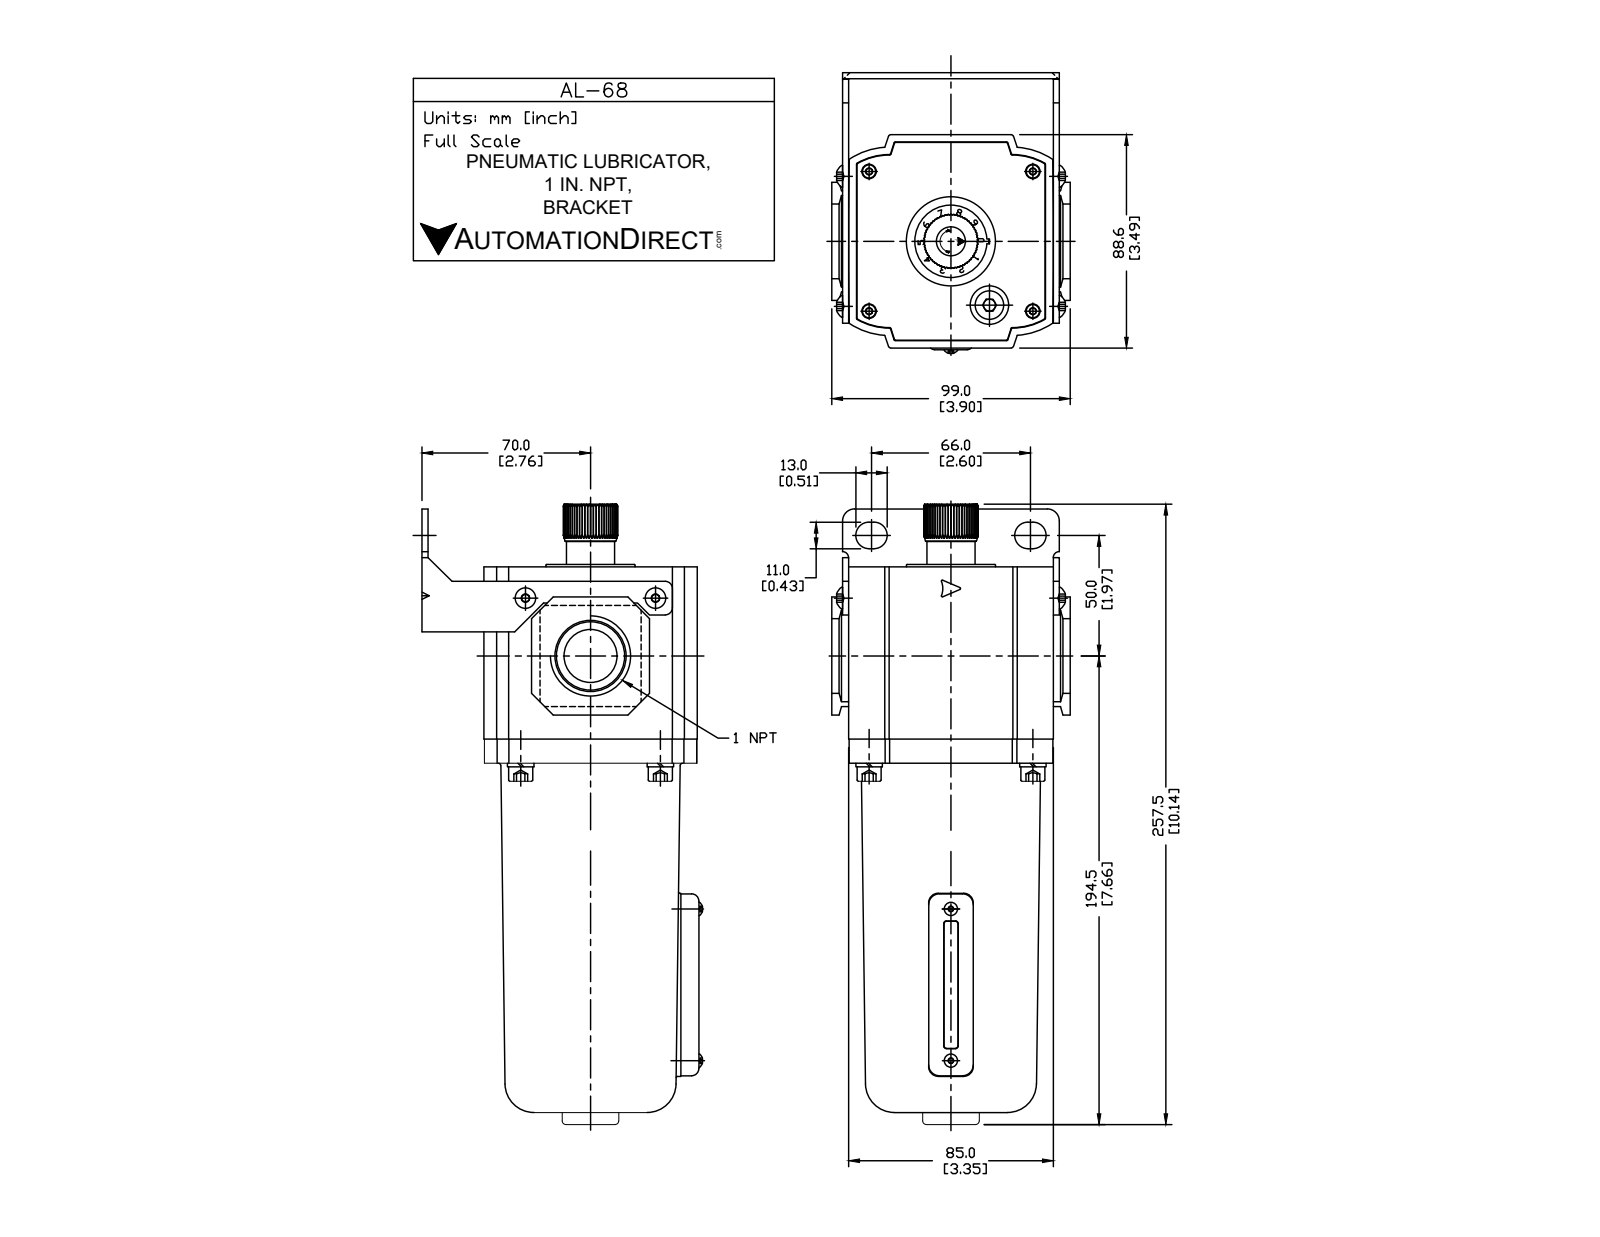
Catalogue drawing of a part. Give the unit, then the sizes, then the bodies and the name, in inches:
Units: inches
Overall size (bounding box): 10.138 × 4.586 × 3.898
Round holes (diameter × count): ⌀0.217 ×2, ⌀1.141 ×1
Round bosses / shafts (diameter × count): ⌀0.394 ×4, ⌀2.933 ×1, ⌀2.362 ×1, ⌀0.925 ×1, ⌀0.787 ×1
Partial cylindrical surfaces — rounded edges, fillets, slot ends (radius × count): R0.118 ×10, R0.079 ×5, R0.012 ×4, R0.039 ×4, R0.217 ×4, R1.169 ×4, R1.181 ×4, R0.008 ×3
Main face-to-face distances: 0.098, 2.815, 3.445, 1.012, 0.913, 4.5, 4.402, 3.488, 0.276, 3.346
Hole centre spacings: 1.422, 2.126
Volume: 74.82 in³ · Surface area: 179.8 in²
Bodies: 6 solids, 570 faces (343 planar, 109 cylindrical, 118 other)
Part name (STEP PRODUCT): AL-68
STEP written by: SolidWorks 2015 (CONFIG_CONTROL_DESIGN)
